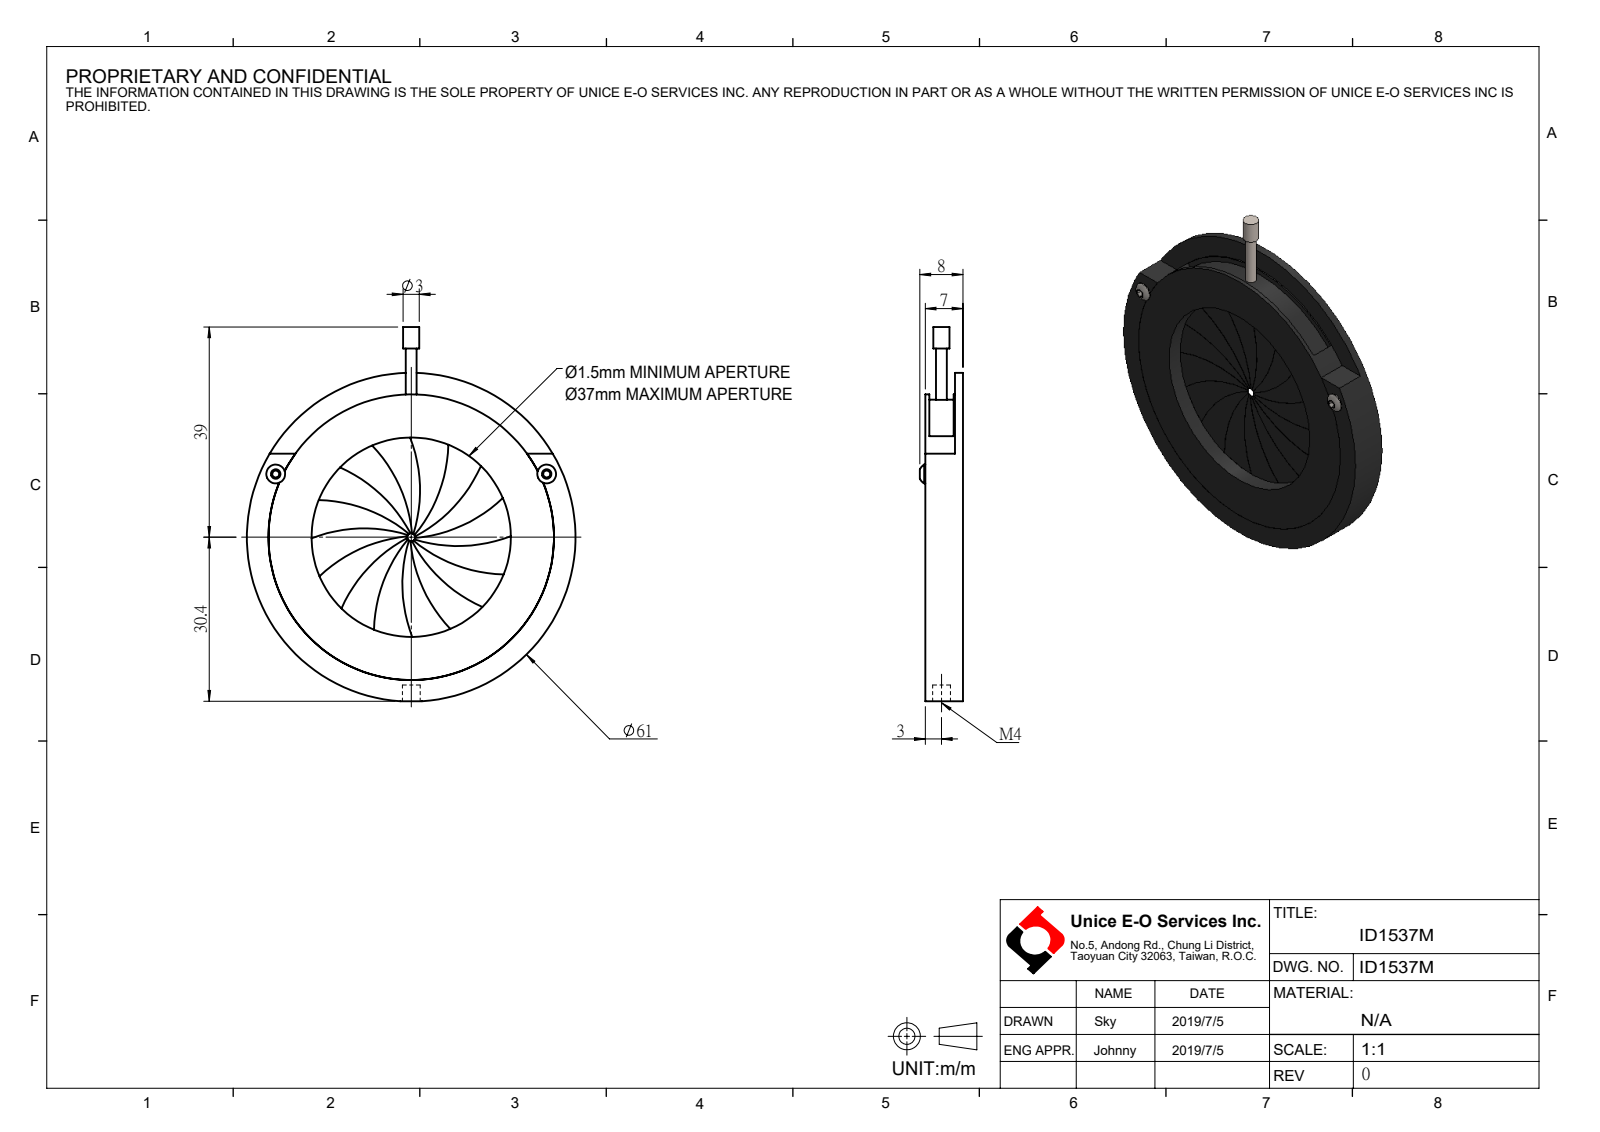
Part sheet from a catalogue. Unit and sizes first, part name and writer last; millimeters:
Units: millimetres
Overall size (bounding box): 69.43 × 61 × 8
Round holes (diameter × count): ⌀1.5 ×1, ⌀3.3 ×1, ⌀37 ×1, ⌀50 ×1
Round bosses / shafts (diameter × count): ⌀3.5 ×2, ⌀61 ×1, ⌀53 ×1, ⌀3 ×1, ⌀2 ×1
Partial cylindrical surfaces — rounded edges, fillets, slot ends (radius × count): R27.19 ×16, R25.5 ×1
Main face-to-face distances: 6, 2.9, 3.1, 2.95, 3.05, 1, 7, 4.1, 3.9, 4.05
Bodies: 0 solids, 122 faces (60 planar, 58 cylindrical, 4 other)
Part name (STEP PRODUCT): ID1537M
STEP written by: SolidWorks 2016 (AUTOMOTIVE_DESIGN)
